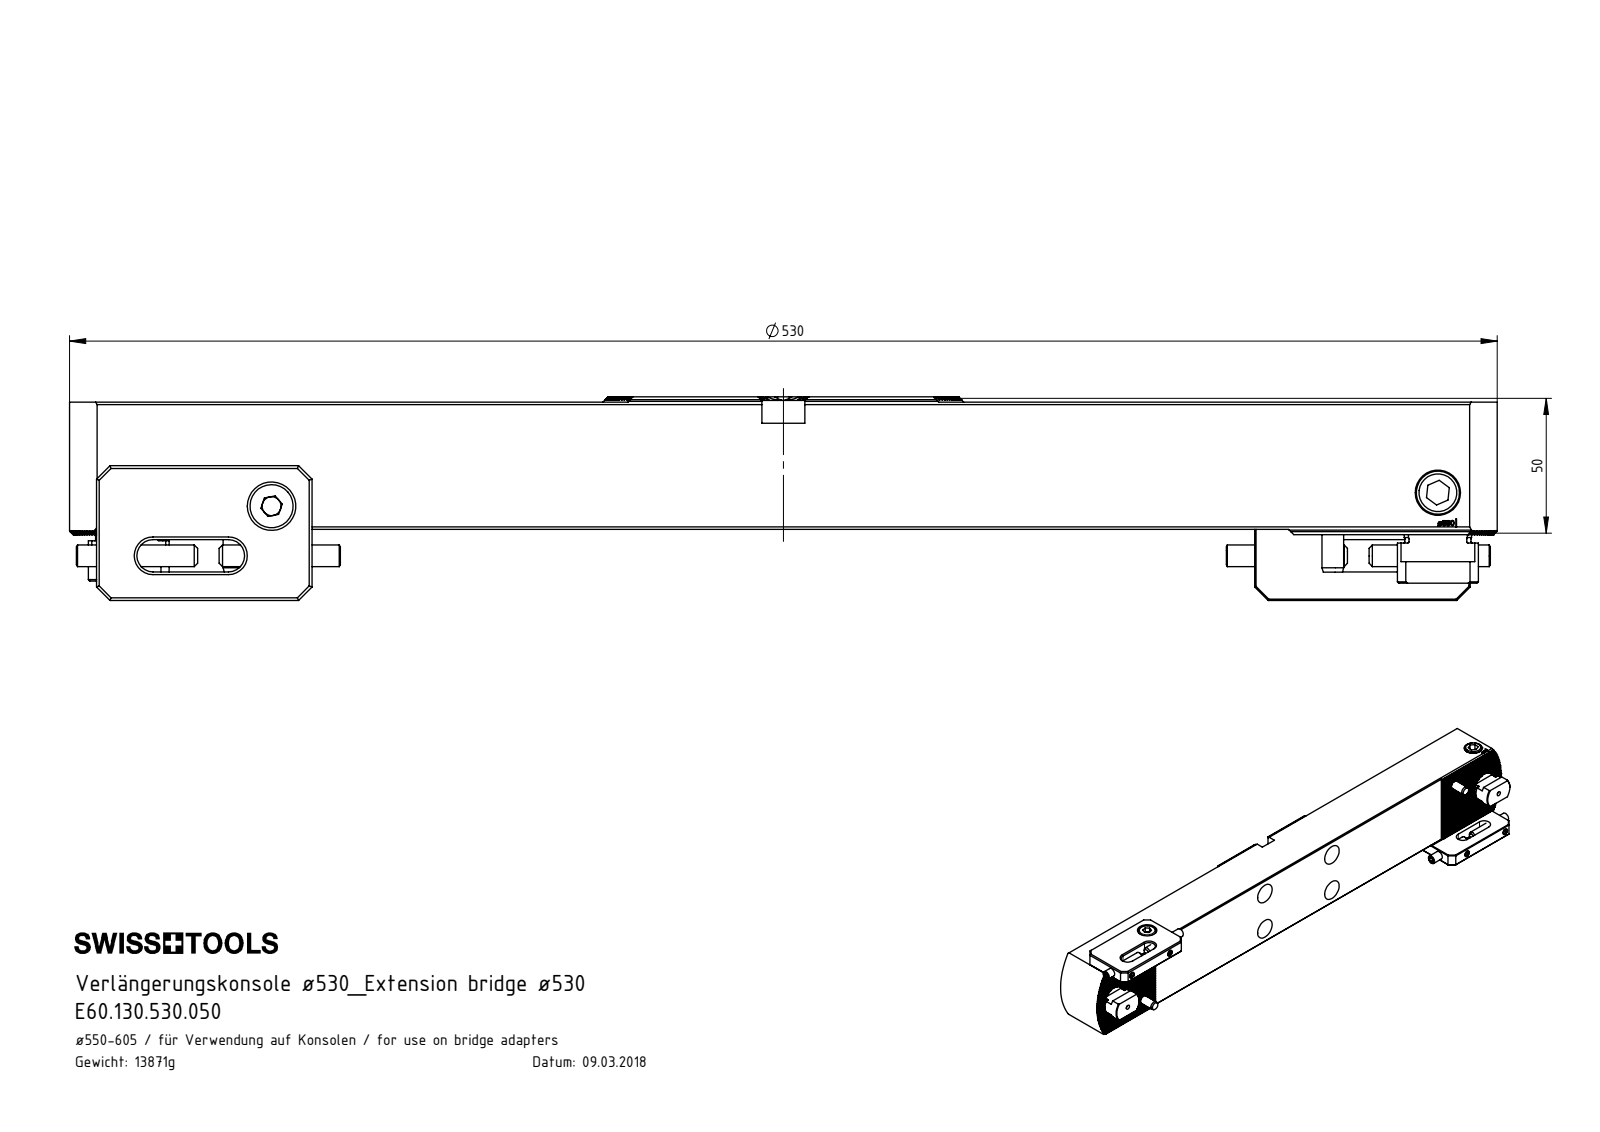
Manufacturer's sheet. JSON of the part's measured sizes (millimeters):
{"part_name": "VK1-ER2.201.010_A_gespannt; VK1-ER2.101.010_A; VK1-ER2.001.044_A; E60.130.530.050 (+8 more)", "step_written_by": "SolidWorks 2017 (CONFIG_CONTROL_DESIGN)", "units": "millimeters", "bodies": {"solids": 27, "faces": 1575, "planar": 874, "cylindrical": 402, "other": 299}, "overall_size": [530, 94, 75.58], "volume_mm3": 1773000, "surface_area_mm2": 214241, "round_holes": [[5, 4], [6, 4], [6.8, 4], [13, 4], [19, 4], [2, 2], [8, 2], [8.5, 2], [10.5, 2], [11, 2], [14, 2], [18, 2]], "round_bosses_or_shafts": [[16, 4], [6, 4], [10, 2], [8, 2]], "partial_cylinders_radius": [[0.14, 66], [2, 8], [6, 4], [12.3, 2], [15, 2], [65, 2], [7.95, 1]], "face_to_face_distances": [47.16, 70, 12, 82, 1.73, 8.66, 3.46, 6.93, 0.5, 41.57], "hole_center_spacings": [486, 200, 287.7, 7.9, 18.55, 19.61, 34.53, 35.09]}
